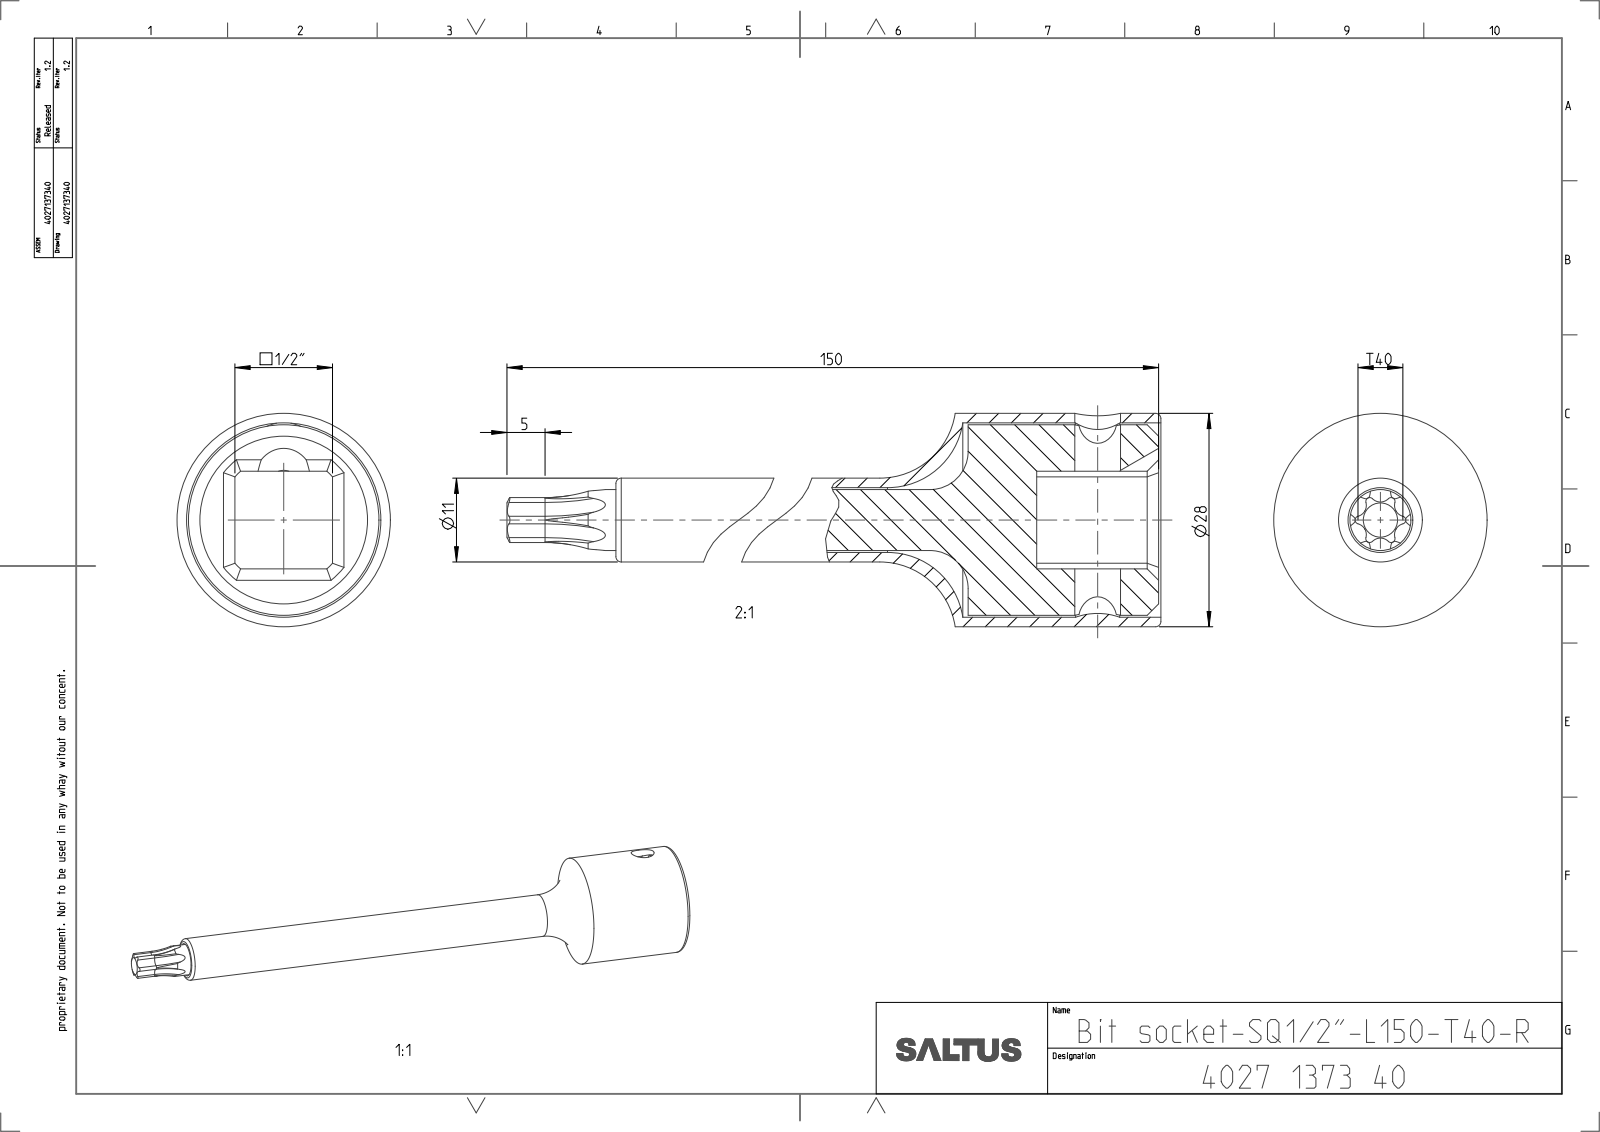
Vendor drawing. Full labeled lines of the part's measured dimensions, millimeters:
Part name (STEP PRODUCT): 4027132840; 4027299345; 4027137340_ASM
STEP written by: CREO PARAMETRIC BY PTC INC, 2022414 (CONFIG_CONTROL_DESIGN)
Units: millimetres
Bodies: 2 solids, 105 faces (15 planar, 45 cylindrical, 45 other)
Overall size (bounding box): 150.3 × 28 × 28
Volume: 22 614 mm³ · Surface area: 18 871 mm²
Round holes (diameter × count): ⌀6 ×1, ⌀8.5 ×1, ⌀25.5 ×1
Round bosses / shafts (diameter × count): ⌀28 ×1, ⌀25 ×1, ⌀11 ×1, ⌀8 ×1
Partial cylindrical surfaces — rounded edges, fillets, slot ends (radius × count): R0.51 ×6, R1.47 ×6, R3.33 ×1, R4 ×1, R8.55 ×1
Main face-to-face distances: 12.82, 9, 16, 25, 16.3, 25.3, 150.3, 150, 134, 125
